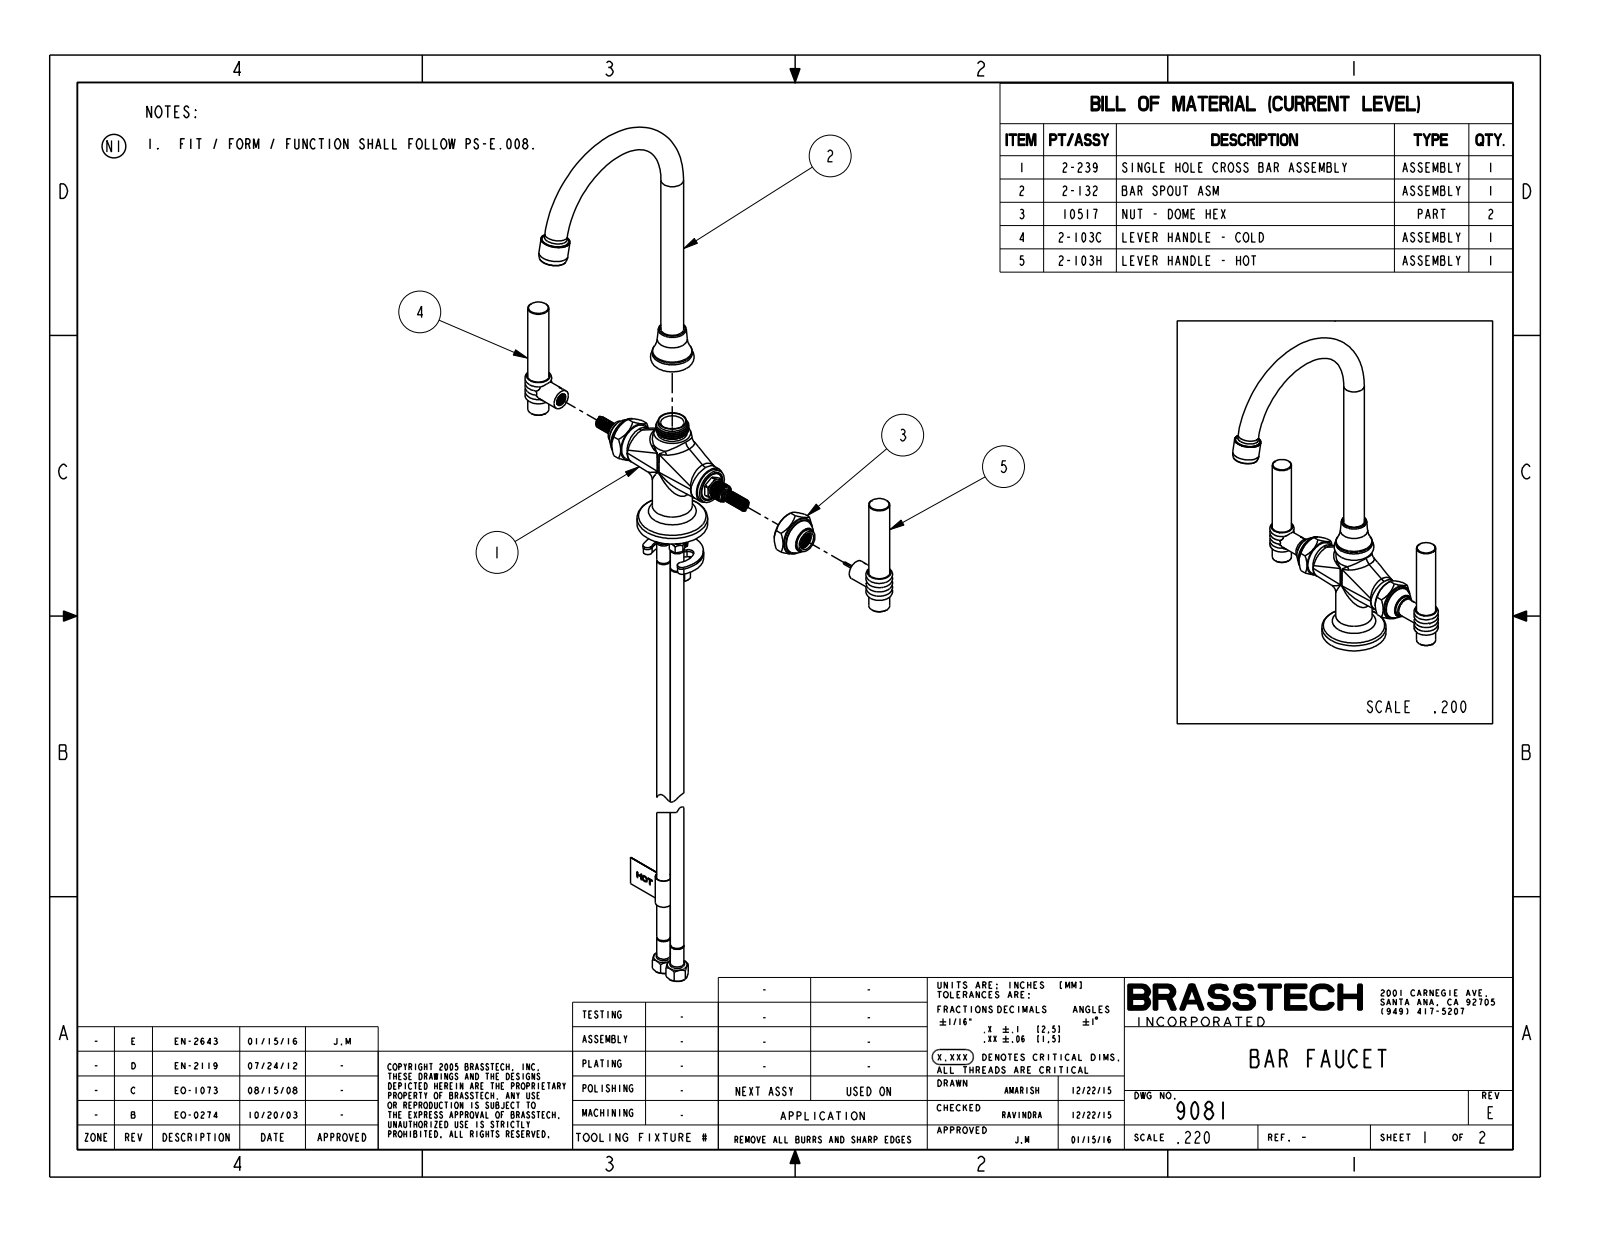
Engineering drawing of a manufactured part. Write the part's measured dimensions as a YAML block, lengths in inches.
part_name: "10230; 1-204; 1-205; 10515 (+8 more)"
step_written_by: "PRO/ENGINEER BY PARAMETRIC TECHNOLOGY CORPORATION, 2009300 (CONFIG_CONTROL_DESIGN)"
units: inches
bodies: {solids: 37, faces: 3558, planar: 984, cylindrical: 1186, other: 1388}
overall_size: [30.96, 7.83, 6.799]
volume: 17.07
surface_area: 403.2
round_holes:
  - {diameter: 0.13, count: 4}
  - {diameter: 0.196, count: 3}
  - {diameter: 0.156, count: 2}
  - {diameter: 0.2, count: 2}
  - {diameter: 0.23, count: 2}
  - {diameter: 0.25, count: 2}
  - {diameter: 0.315, count: 2}
  - {diameter: 0.33, count: 2}
  - {diameter: 0.351, count: 2}
  - {diameter: 0.423, count: 2}
  - {diameter: 0.515, count: 2}
  - {diameter: 0.642, count: 2}
round_bosses_or_shafts:
  - {diameter: 0.164, count: 4}
  - {diameter: 0.706, count: 2}
  - {diameter: 0.656, count: 2}
  - {diameter: 0.55, count: 2}
  - {diameter: 0.473, count: 2}
  - {diameter: 0.42, count: 2}
  - {diameter: 0.38, count: 2}
  - {diameter: 0.375, count: 2}
partial_cylinders:
  - {radius: 0.04, count: 9}
  - {radius: 0.08, count: 8}
  - {radius: 0.14, count: 4}
  - {radius: 0.175, count: 4}
  - {radius: 0.046, count: 2}
  - {radius: 0.05, count: 2}
  - {radius: 0.26, count: 2}
  - {radius: 0.3, count: 2}
face_to_face_distances: [1.1, 1.25, 1.301, 2.509, 0.2, 1.3, 0.272, 0.072, 1.028, 6.614]
hole_center_spacings: [0.311, 0.604, 0.617, 3.201, 3.5, 3.528, 3.53, 3.801]
